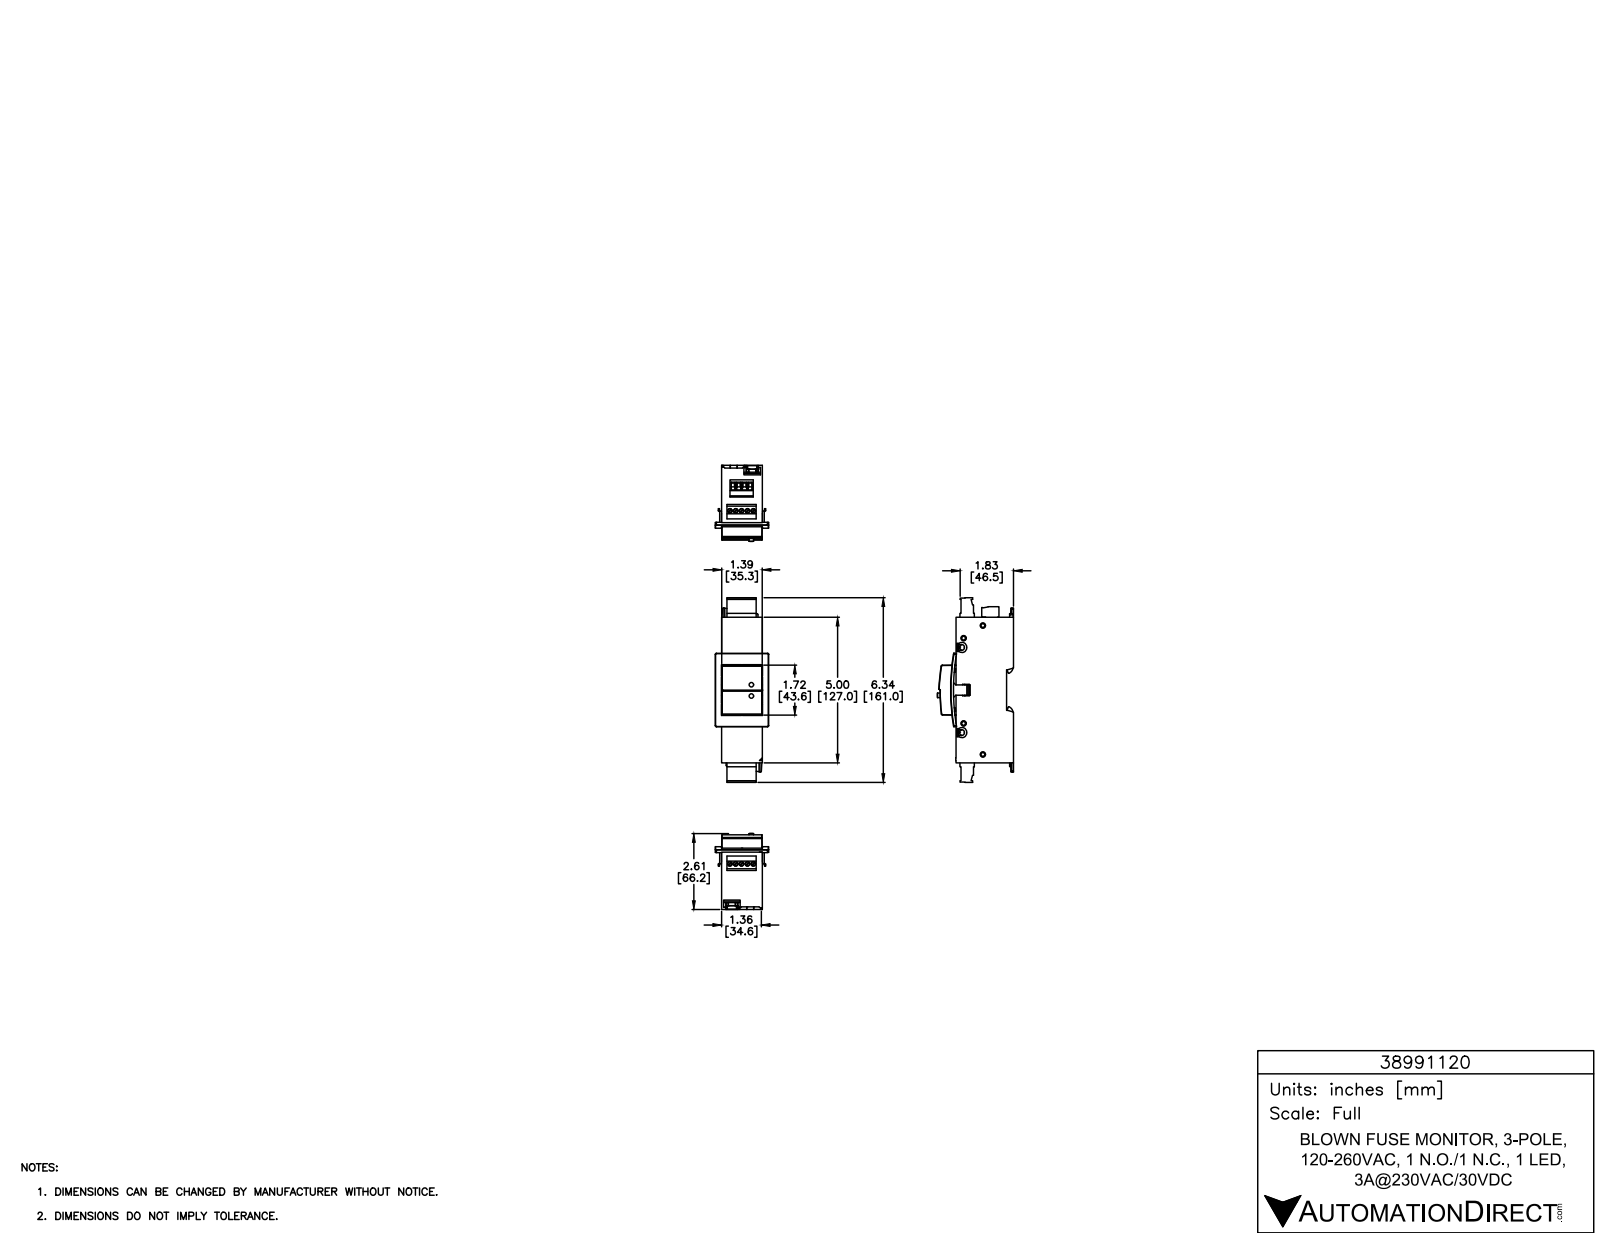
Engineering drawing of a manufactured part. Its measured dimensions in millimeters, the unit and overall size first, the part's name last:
Units: millimetres
Overall size (bounding box): 161 × 66.4 × 46.5
Round holes (diameter × count): ⌀4 ×9, ⌀4.6 ×4, ⌀4.2 ×2
Round bosses / shafts (diameter × count): ⌀3.8 ×9, ⌀4.2 ×4
Partial cylindrical surfaces — rounded edges, fillets, slot ends (radius × count): R0.2 ×24, R0.2 ×24, R0.6 ×24, R1 ×15, R0.3 ×12, R0.5 ×10, R1.2 ×4, R1.5 ×4
Main face-to-face distances: 35.5, 44, 50, 6, 127, 17.8, 10.2, 5.4, 4.3, 39.7
Hole centre spacings: 5.1, 10.2, 15.2, 9.8, 20.1, 20.3, 31.9, 62.7
Volume: 243 300 mm³ · Surface area: 44 520 mm²
Bodies: 1 solid, 847 faces (521 planar, 248 cylindrical, 78 other)
Part name (STEP PRODUCT): 38991120
STEP written by: SolidWorks 2015 (AUTOMOTIVE_DESIGN)
